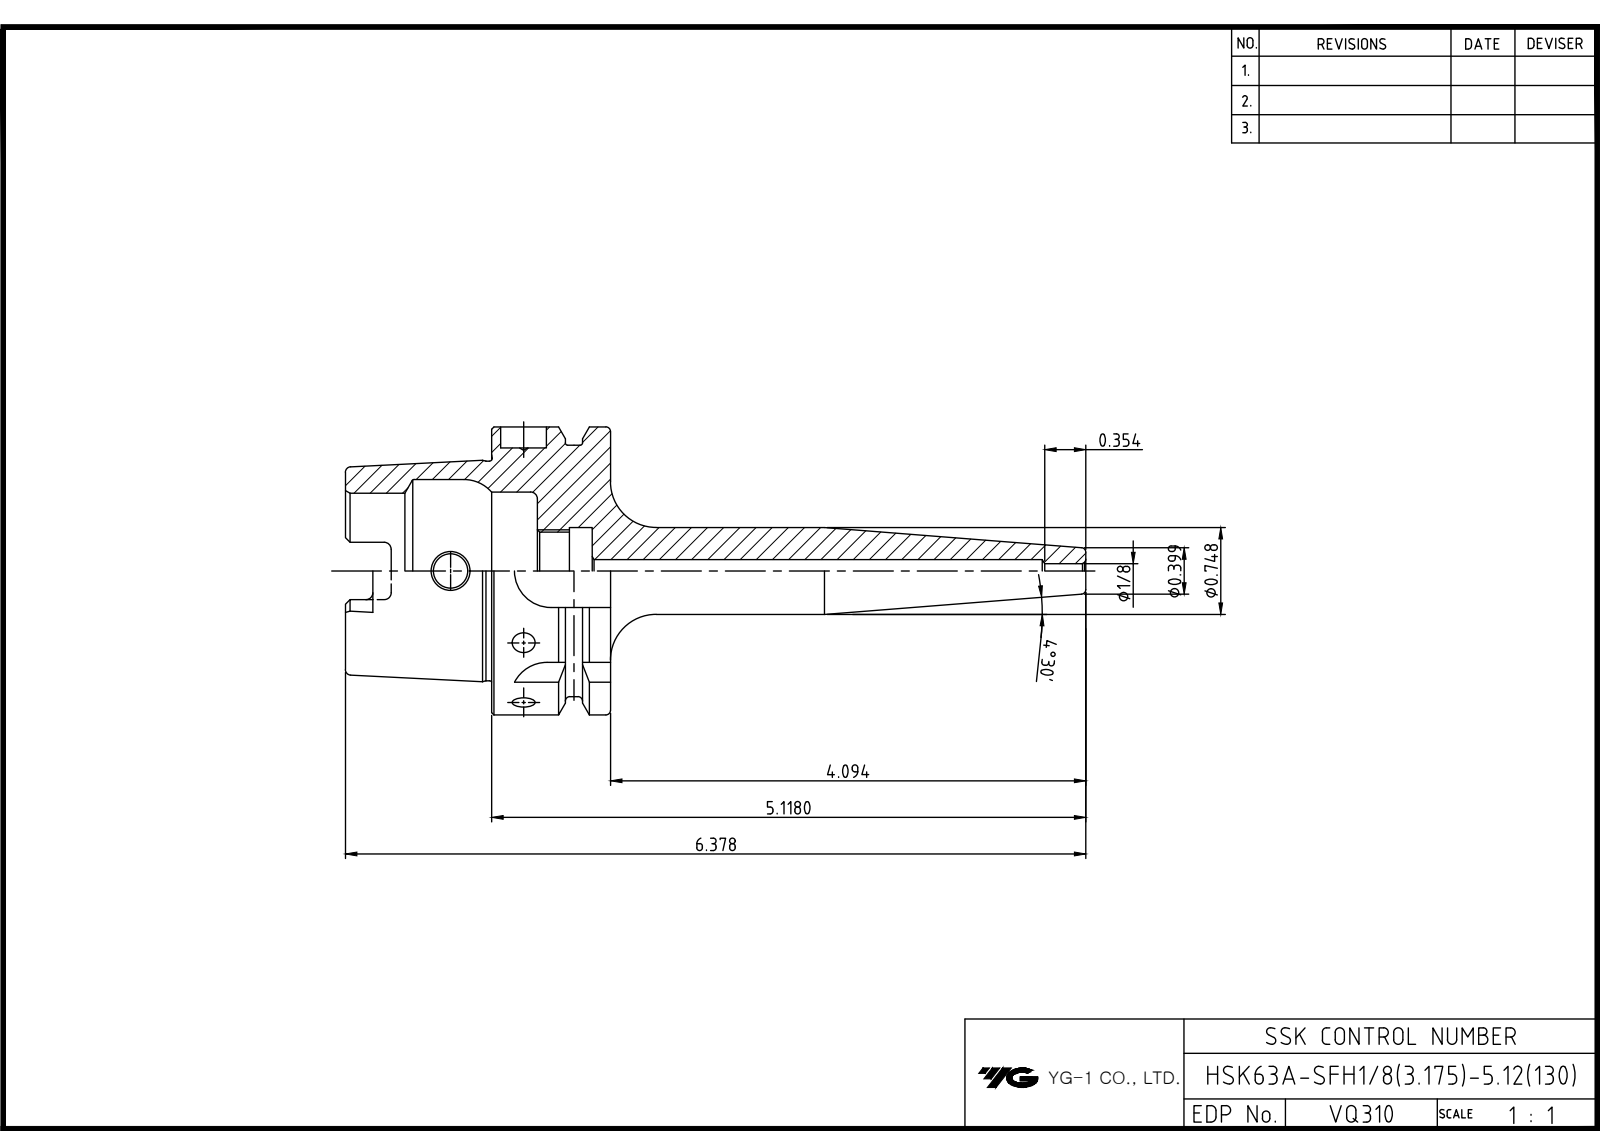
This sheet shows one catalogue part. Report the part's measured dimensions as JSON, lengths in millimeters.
{"part_name": "LO-HSK63A-SFH3.175-130", "step_written_by": "Autodesk Inventor 2022 (AUTOMOTIVE_DESIGN)", "units": "millimeters", "bodies": {"solids": 1, "faces": 114, "planar": 40, "cylindrical": 33, "other": 41}, "overall_size": [162, 63, 63], "volume_mm3": 104026, "surface_area_mm2": 28935, "round_holes": [[3.17, 1], [5, 1], [7.5, 1], [8.4, 1], [10, 1], [16.92, 1], [19, 1], [34, 1], [40, 1]], "round_bosses_or_shafts": [[63, 1], [55, 1], [48.04, 1]], "partial_cylinders_radius": [[1.5, 6], [2.88, 4], [8, 4]], "face_to_face_distances": [26, 10, 16, 32, 42, 58, 53, 22, 4, 12]}
